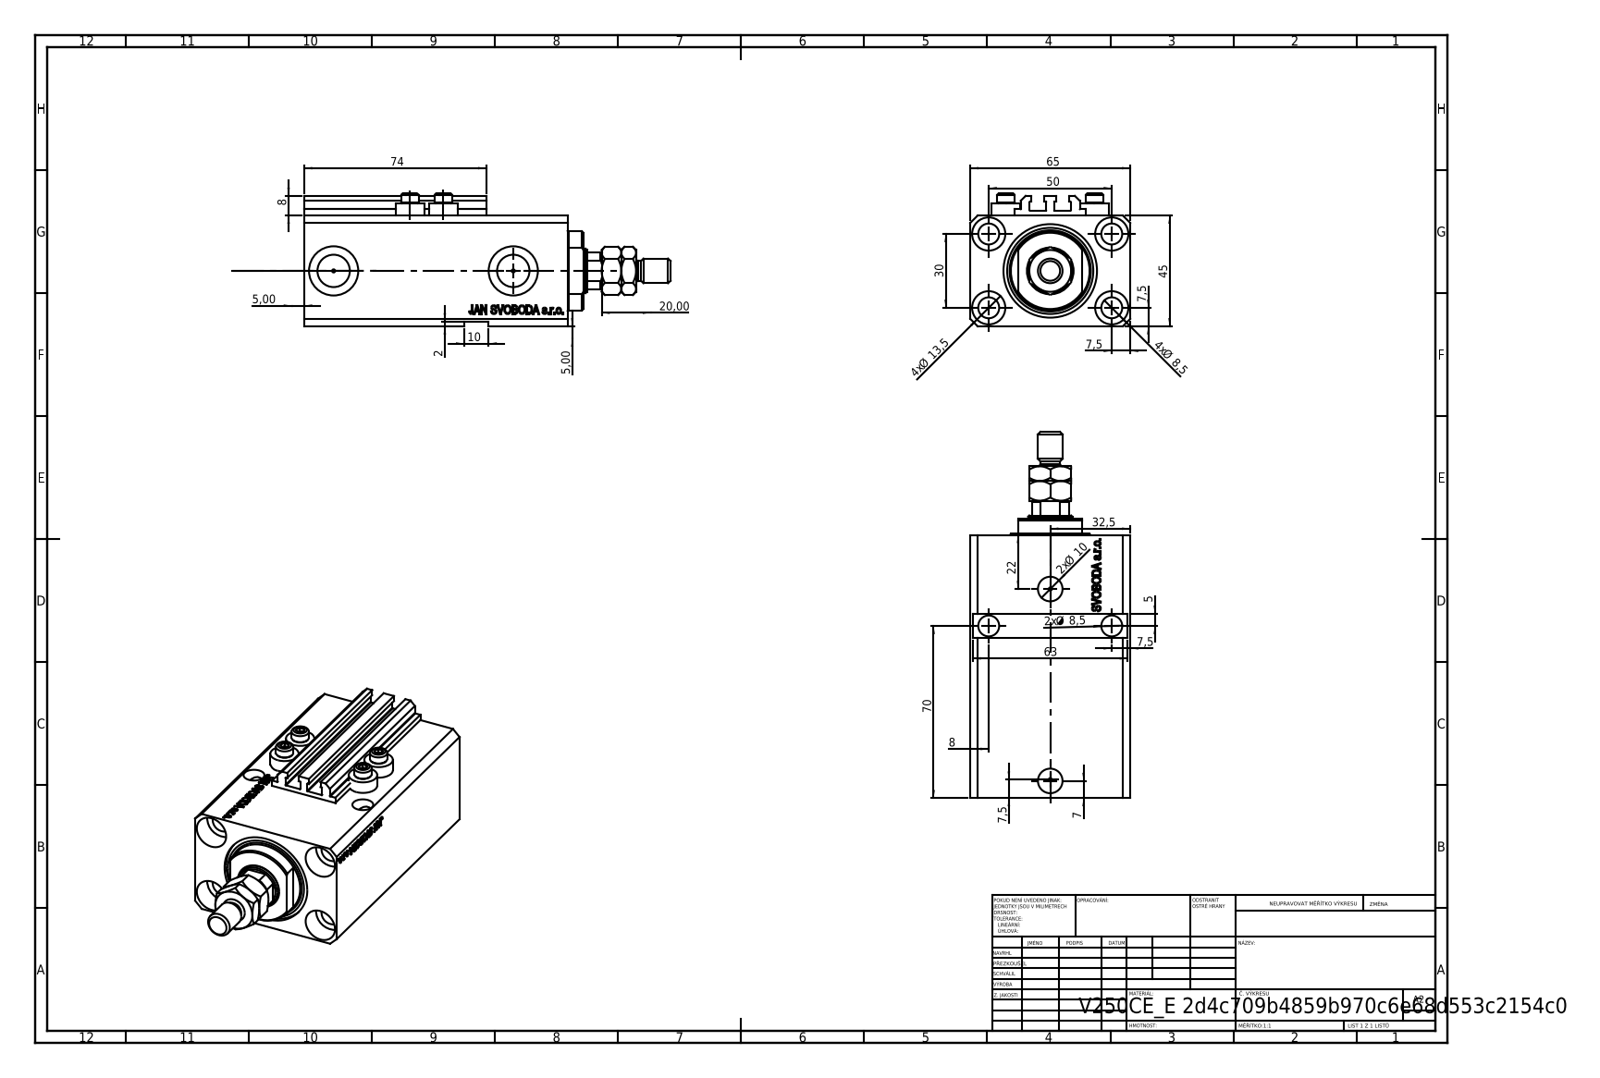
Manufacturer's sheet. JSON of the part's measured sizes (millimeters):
{"part_name": "ALLEN BOLT V250CE; V250CE_C_VCP; V250CE_VC_E; MTA (+1 more)", "step_written_by": "SolidWorks 2019 (CONFIG_CONTROL_DESIGN)", "units": "millimeters", "bodies": {"solids": 9, "faces": 1116, "planar": 526, "cylindrical": 130, "other": 460}, "overall_size": [148.9, 65, 54], "volume_mm3": 281346, "surface_area_mm2": 79699, "round_holes": [[8.5, 7], [1.25, 4], [4, 4], [13.5, 4], [10, 2], [13.16, 2], [20, 2], [18, 1], [25, 1], [38, 1]], "round_bosses_or_shafts": [[11.6, 4], [7, 4], [10, 1], [8, 1]], "partial_cylinders_radius": [[0.2, 10], [8.5, 1], [16, 1]], "face_to_face_distances": [45, 65, 81.9, 2, 47, 6.9, 107, 25.1, 2.5, 75], "hole_center_spacings": [29.15, 50, 13.6, 15.12, 27.89, 30, 33.62, 36]}
